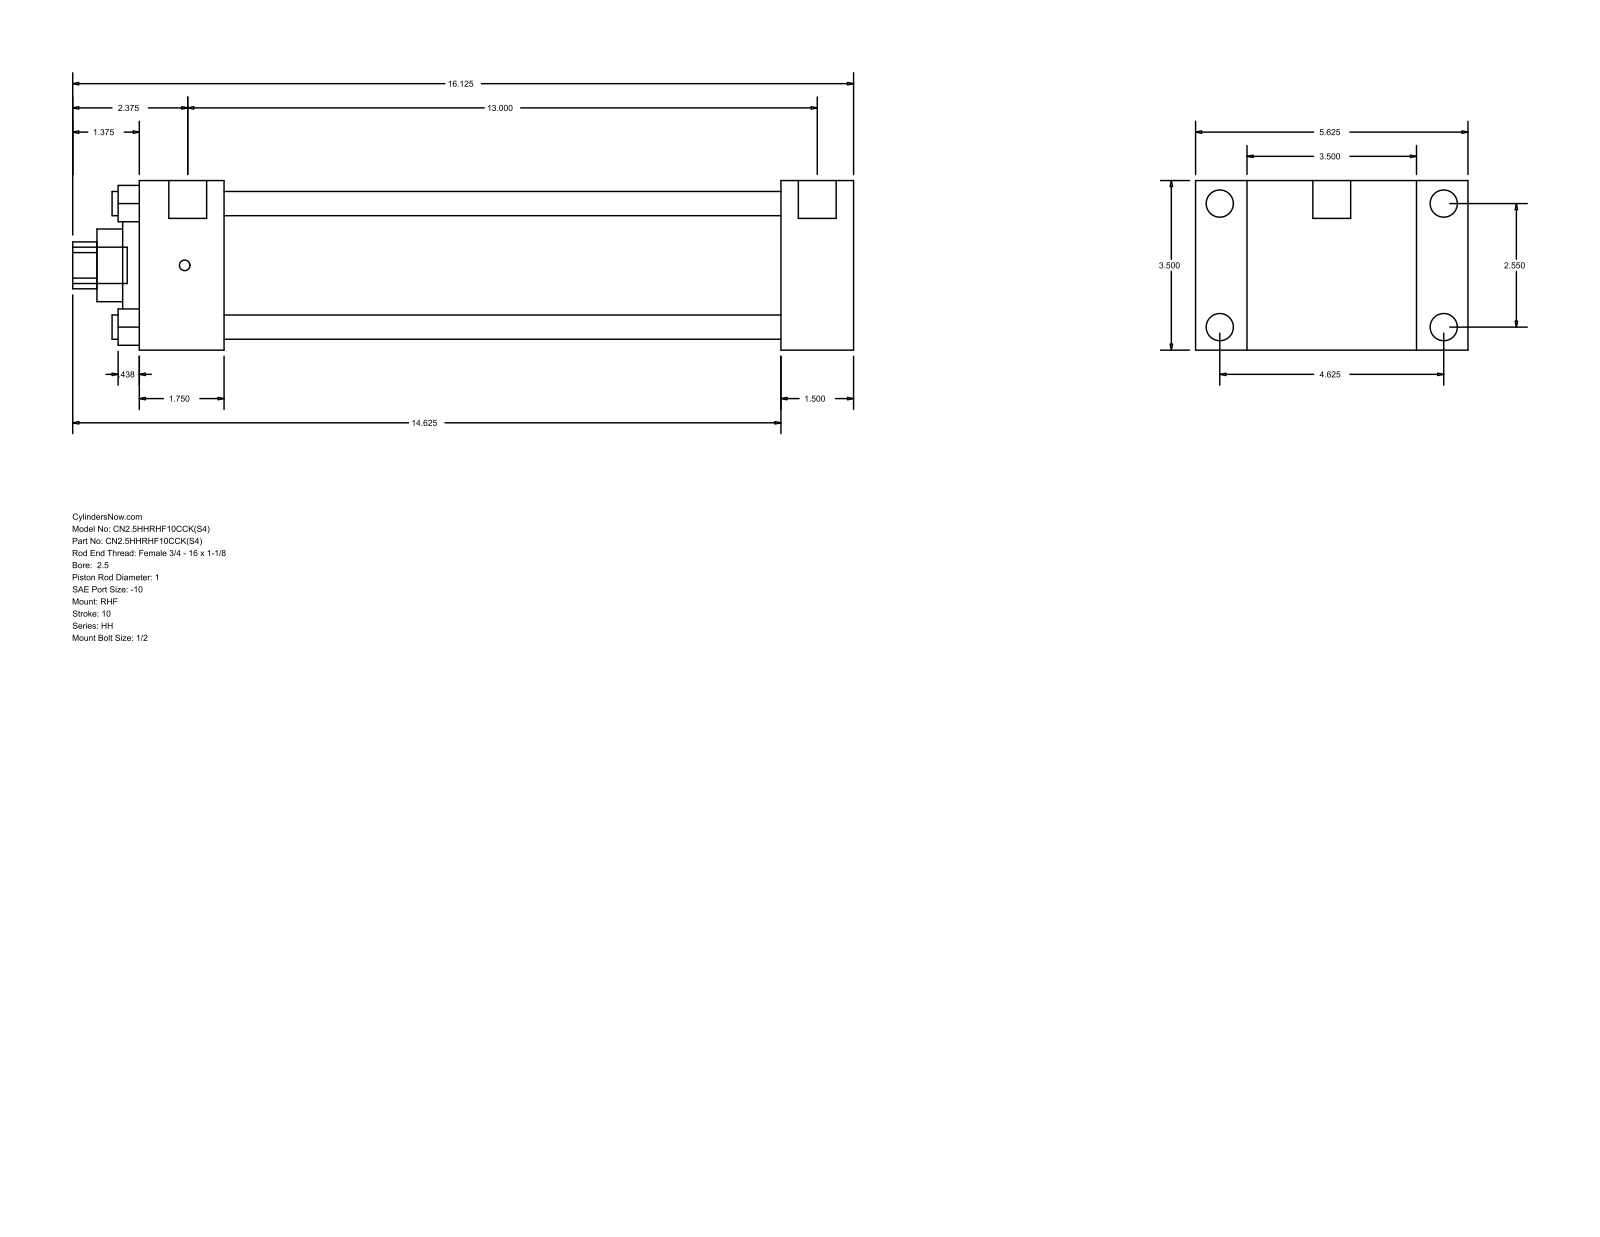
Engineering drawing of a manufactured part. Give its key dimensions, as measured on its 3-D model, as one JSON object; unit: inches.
{"part_name": "HH_RHF__0250_1", "step_written_by": "GSSL Pune (CONFIG_CONTROL_DESIGN)", "units": "inches", "bodies": {"solids": 0, "faces": 90, "planar": 61, "cylindrical": 29, "other": 0}, "overall_size": [16.125, 5.625, 3.5], "round_holes": [[0.5, 4], [1, 1], [1.5, 1], [2.375, 1], [2.875, 1]], "round_bosses_or_shafts": [[0.563, 4], [0.219, 4], [0.781, 2], [0.75, 1]], "partial_cylinders_radius": [[0.484, 1]], "face_to_face_distances": [3.5, 1.5, 1.063, 4.563, 13.25, 14.75, 5.625, 1.75, 11.5, 13], "hole_center_spacings": [1.803, 2.55, 3.606]}
